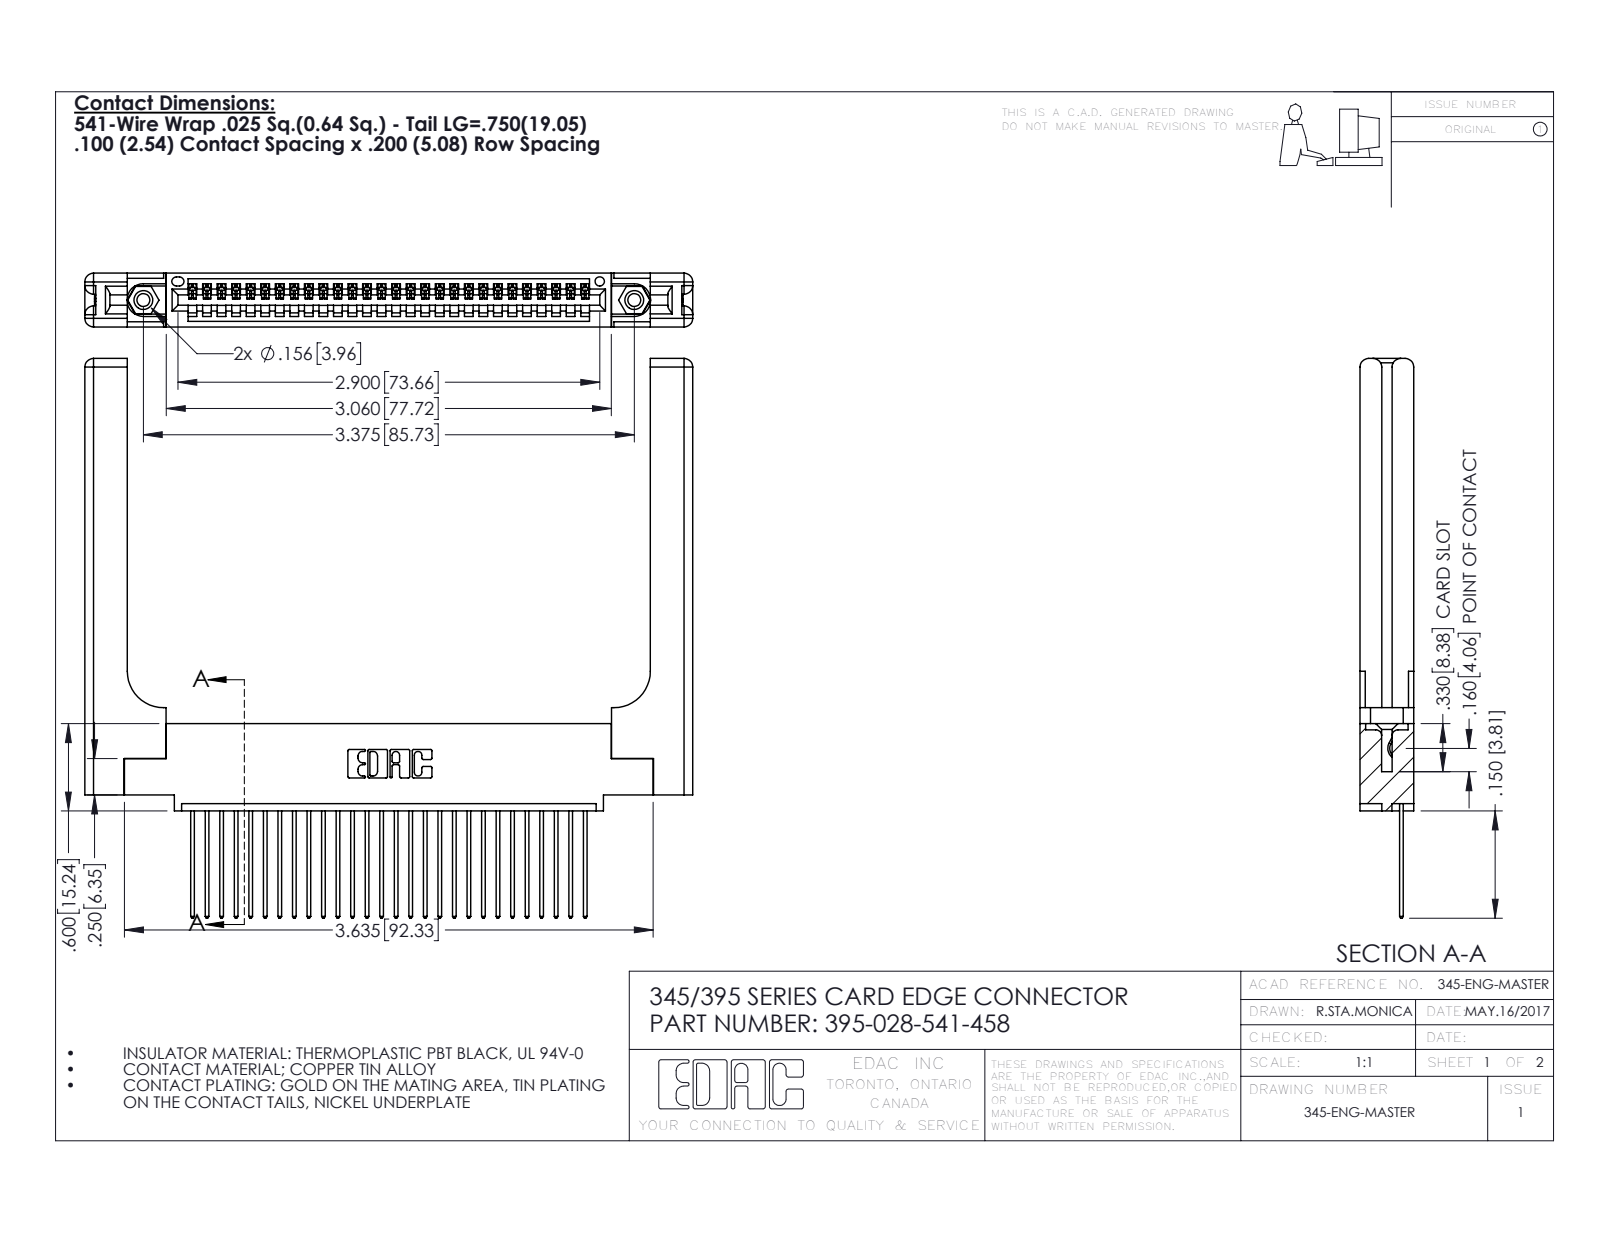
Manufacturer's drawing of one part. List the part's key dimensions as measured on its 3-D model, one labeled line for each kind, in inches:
Part name (STEP PRODUCT): 345 Part_0.110 Offset - 0.156 Dia-TH; 345-220-058_345-220-058; 345-292-001_345-293-141; 395-028-541-458 (+1 more)
STEP written by: SolidWorks 2016 (CONFIG_CONTROL_DESIGN)
Units: inches
Bodies: 33 solids, 2010 faces (1352 planar, 598 cylindrical, 60 other)
Overall size (bounding box): 4.179 × 3.847 × 0.37
Volume: 1.128 in³ · Surface area: 29.47 in²
Round holes (diameter × count): ⌀0.089 ×2, ⌀0.125 ×2, ⌀0.156 ×2, ⌀0.064 ×1
Round bosses / shafts (diameter × count): ⌀0.155 ×2
Partial cylindrical surfaces — rounded edges, fillets, slot ends (radius × count): R0.006 ×56, R0.01 ×56, R0.01 ×22, R0.06 ×16, R0.007 ×6, R0.031 ×6, R0.026 ×3, R0.03 ×2
Main face-to-face distances: 0.37, 0.072, 0.298, 0.098, 0.272, 0.025, 0.2, 0.148, 0.15, 0.077
Hole centre spacings: 0.27, 3.14, 3.375
